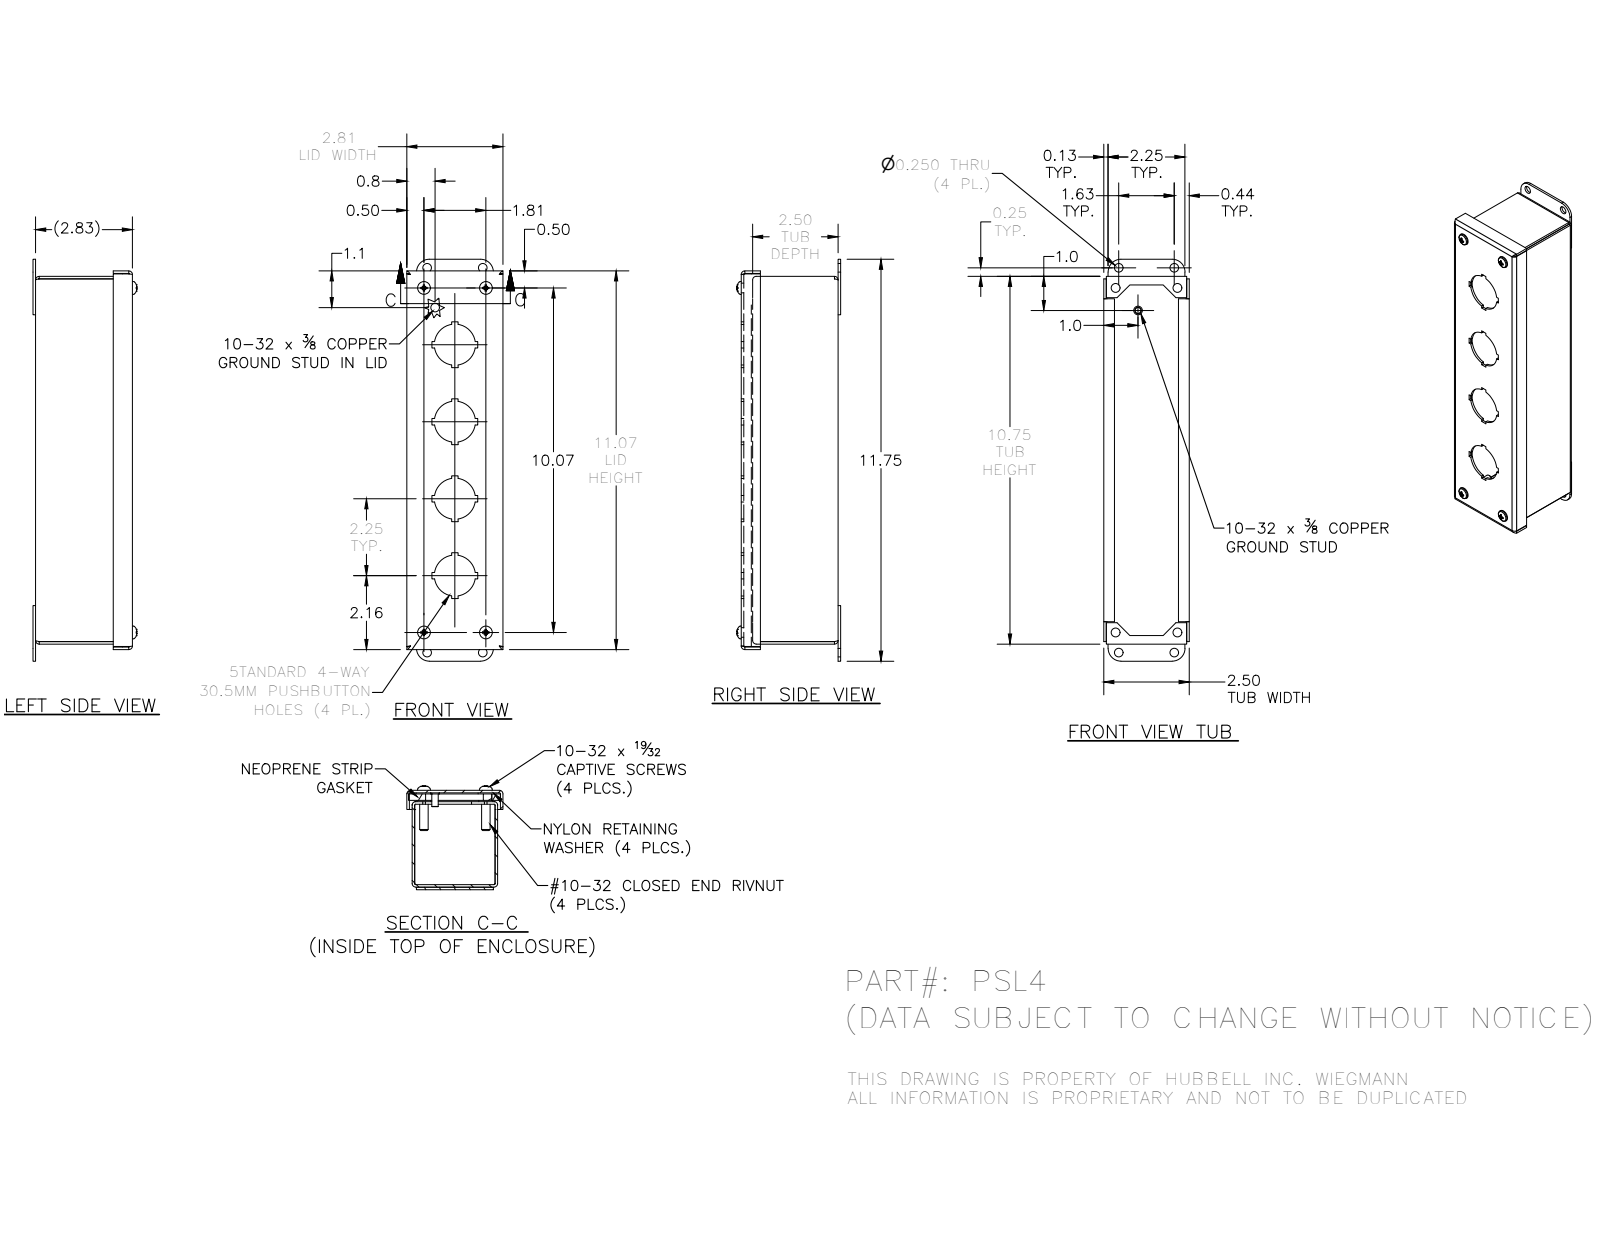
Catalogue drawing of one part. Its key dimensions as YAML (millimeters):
part_name: "PSL4LID; 372163; 39077; PSL4BKP (+5 more)"
step_written_by: "Autodesk Inventor 2016 (AUTOMOTIVE_DESIGN)"
units: millimeters
bodies: {solids: 20, faces: 552, planar: 326, cylindrical: 112, other: 114}
overall_size: [298.45, 77.11, 71.37]
volume: 214293
surface_area: 216270
round_holes:
  - {diameter: 3.96, count: 4}
  - {diameter: 4.98, count: 4}
  - {diameter: 6.35, count: 4}
  - {diameter: 6.53, count: 4}
  - {diameter: 7.06, count: 4}
  - {diameter: 7.14, count: 4}
  - {diameter: 7.95, count: 4}
  - {diameter: 30.48, count: 4}
round_bosses_or_shafts:
  - {diameter: 4.83, count: 6}
  - {diameter: 11.51, count: 4}
  - {diameter: 10.31, count: 4}
  - {diameter: 9.47, count: 4}
  - {diameter: 6.3, count: 4}
  - {diameter: 6.35, count: 2}
partial_cylinders:
  - {radius: 0.79, count: 12}
  - {radius: 2.67, count: 12}
  - {radius: 2.27, count: 4}
  - {radius: 9.53, count: 4}
face_to_face_distances: [1.88, 61.62, 70.05, 63.5, 71.93, 59.74, 68.17, 4.78, 7.47, 2.69]
hole_center_spacings: [116.15, 172.69, 229.53, 48.02, 57.15, 101.94, 158.14, 259.88]
